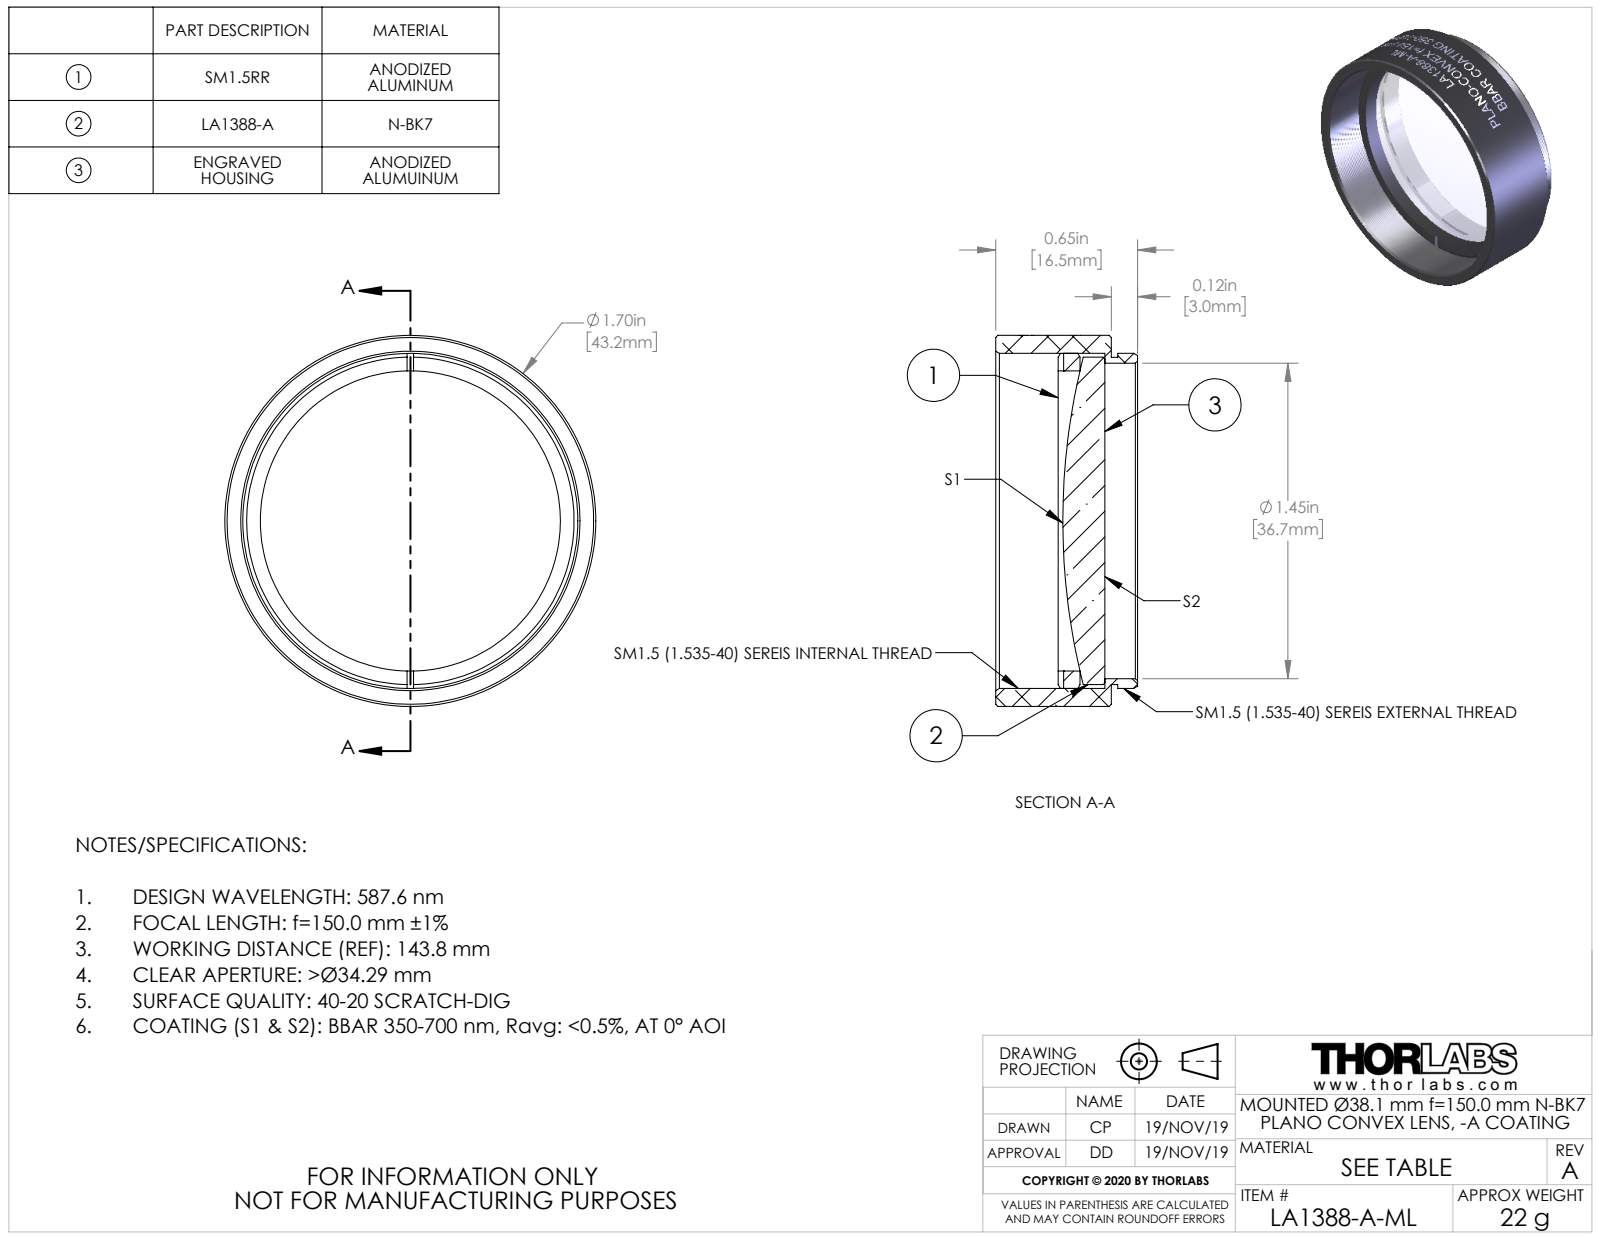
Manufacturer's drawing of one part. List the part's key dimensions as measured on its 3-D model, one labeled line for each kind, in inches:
Part name (STEP PRODUCT): TTN200723-E0W
STEP written by: SolidWorks 2018 (CONFIG_CONTROL_DESIGN)
Units: inches
Bodies: 3 solids, 160 faces (15 planar, 126 cylindrical, 19 other)
Overall size (bounding box): 1.7 × 1.7 × 0.65
Volume: 0.542 in³ · Surface area: 13.35 in²
Round holes (diameter × count): ⌀1.375 ×1, ⌀1.445 ×1
Round bosses / shafts (diameter × count): ⌀1.7 ×1, ⌀1.535 ×1, ⌀1.5 ×1, ⌀1.499 ×1
Main face-to-face distances: 0.03, 0.53, 0.5, 0.144, 0.114, 0.386, 0.244, 0.214, 0.1, 0.286
